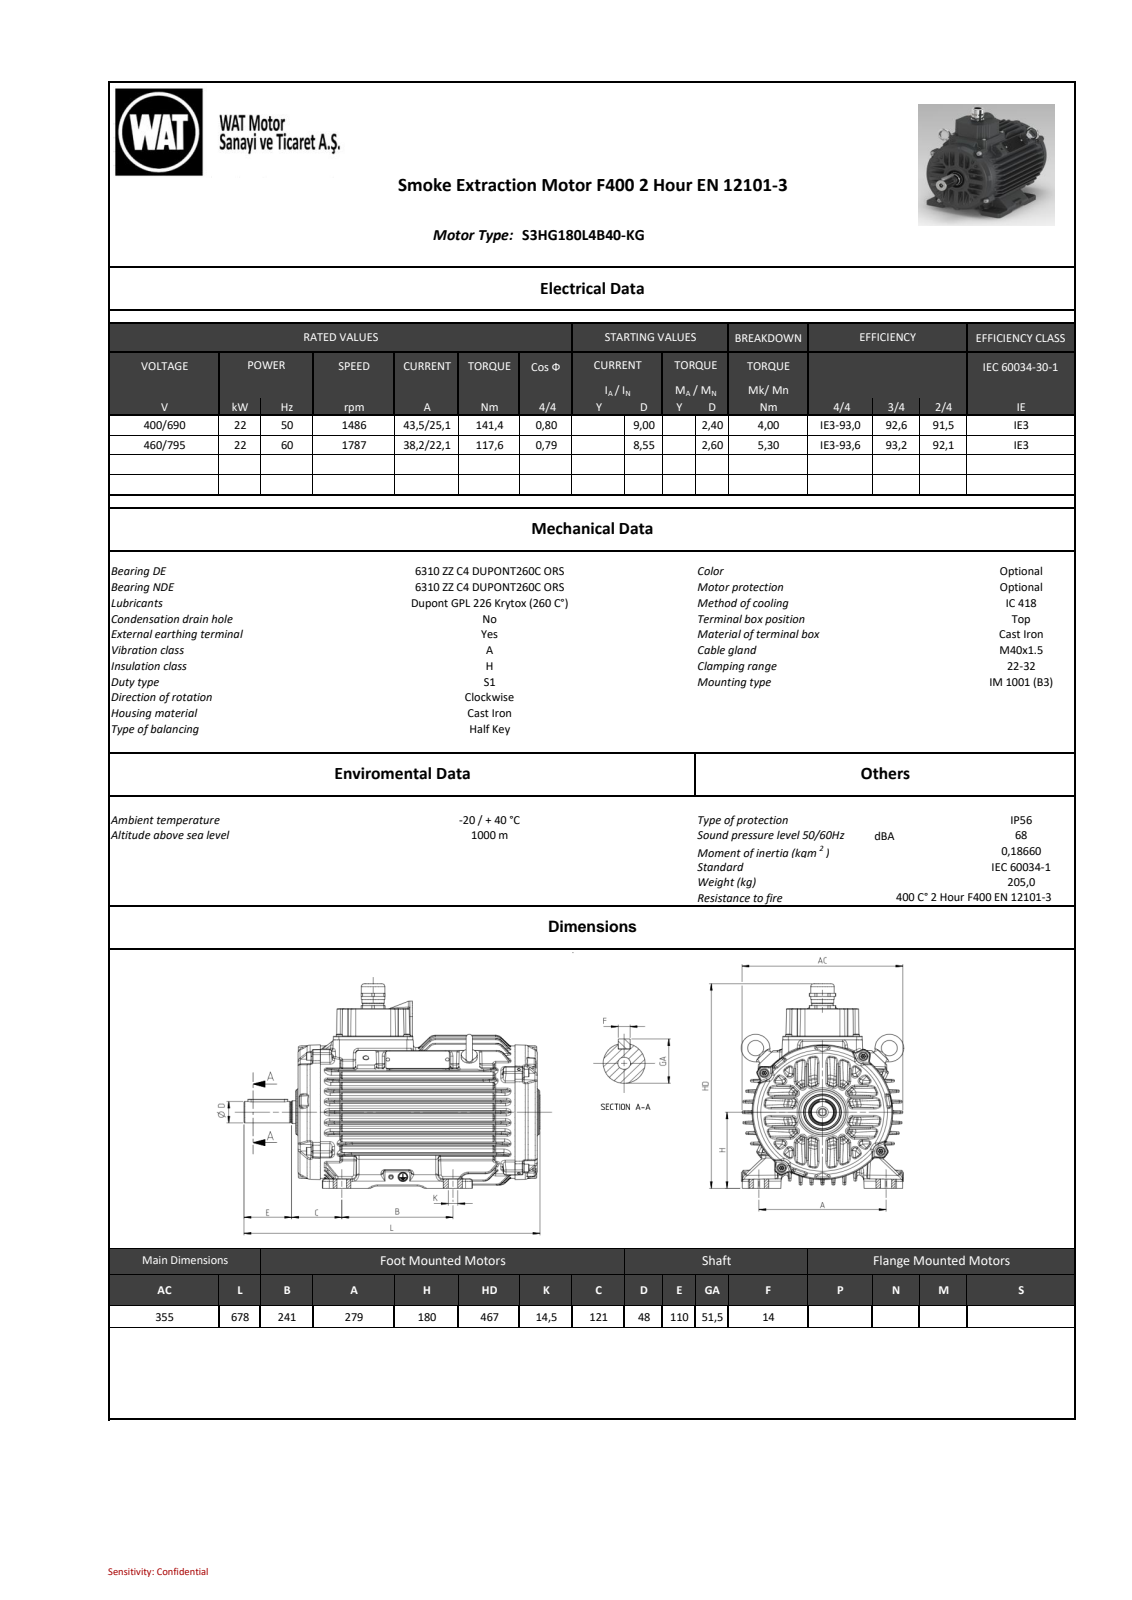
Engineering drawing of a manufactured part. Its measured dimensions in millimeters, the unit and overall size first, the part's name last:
Units: millimetres
Overall size (bounding box): 678 × 467 × 355.28
Round holes (diameter × count): ⌀9 ×8, ⌀5 ×4, ⌀2.5 ×2, ⌀10.9 ×2, ⌀6.8 ×1, ⌀14 ×1, ⌀17 ×1, ⌀32 ×1, ⌀62 ×1, ⌀75.8 ×1, ⌀76 ×1
Round bosses / shafts (diameter × count): ⌀20 ×4, ⌀16 ×4, ⌀15.73 ×4, ⌀12 ×4, ⌀30 ×2, ⌀18.1 ×2, ⌀310 ×1, ⌀80 ×1
Partial cylindrical surfaces — rounded edges, fillets, slot ends (radius × count): R4 ×389, R3 ×186, R1.5 ×136, R2 ×87, R5 ×82, R1.8 ×64, R0.4 ×29, R10 ×19
Main face-to-face distances: 14.54, 14.46, 29, 29.14, 14.6, 43.6, 58.71, 58.25, 43.79, 29.25
Hole centre spacings: 223.45, 54.7, 158, 158.01, 181.4, 258.76, 311.24, 316.01
Bodies: 0 solids, 6961 faces (959 planar, 1651 cylindrical, 4351 other)
Part name (STEP PRODUCT): 26032C0836B7xlc7
STEP written by: SIEMENS PLM Software NX 11.0 (AUTOMOTIVE_DESIGN)
